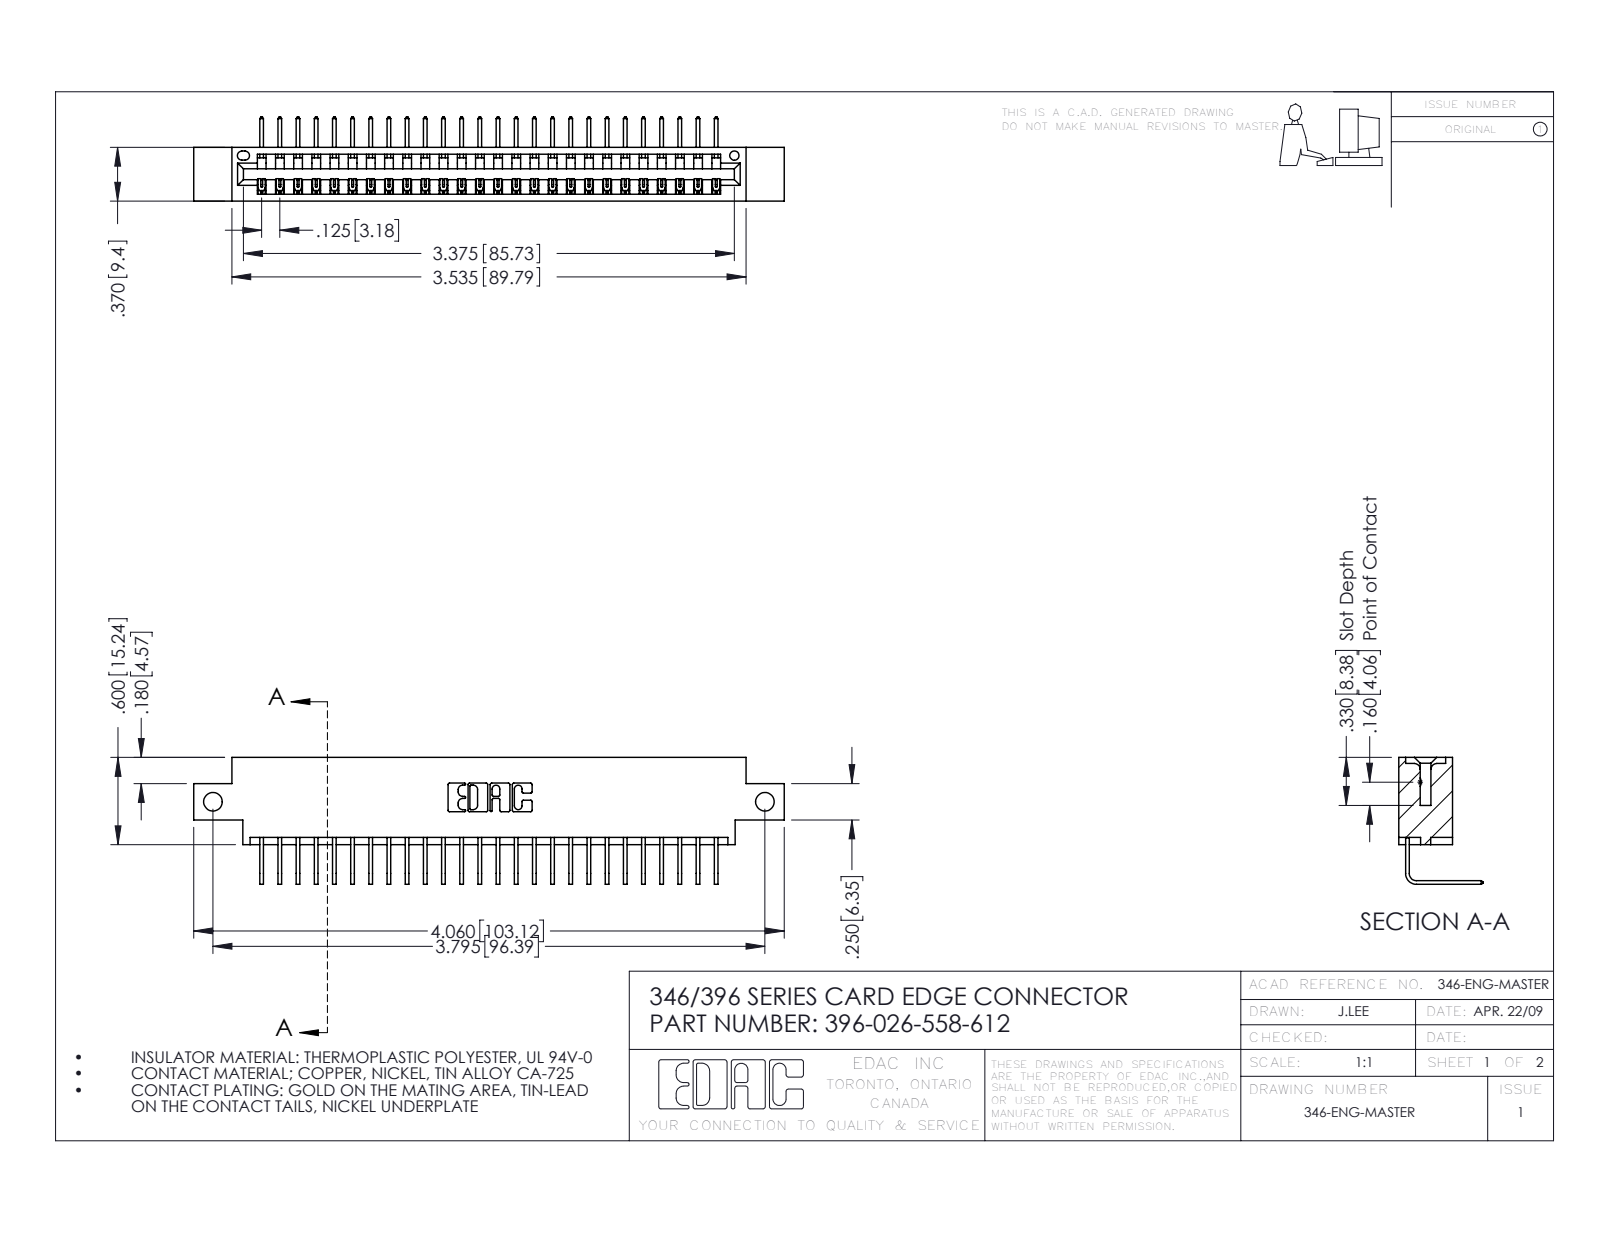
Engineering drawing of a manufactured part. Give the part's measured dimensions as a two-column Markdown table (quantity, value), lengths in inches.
| quantity | value |
| --- | --- |
| part name | 345-292-001_558 Tail - 2; 396-026-558-612; 346 Part_0.170 Offset - Side Mount |
| STEP written by | SolidWorks 2016 (CONFIG_CONTROL_DESIGN) |
| units | inches |
| bodies | 27 solids, 1686 faces (1172 planar, 514 cylindrical, 0 other) |
| overall size | 4.06 × 0.873 × 0.58 |
| volume | 0.586 in³ |
| surface area | 19.17 in² |
| round holes (diameter × count) | 0.128 × 2, 0.064 × 1 |
| partial cylindrical surfaces (radius × count) | 0.006 × 52, 0.01 × 22, 0.007 × 6, 0.031 × 6, 0.026 × 3, 0.031 × 2, 0.04 × 2, 0.014 × 1 |
| main face-to-face distances | 0.322, 0.048, 0.37, 0.25, 0.298, 0.025, 0.072, 0.148, 0.222, 0.1 |
| hole center spacings | 3.795 |
